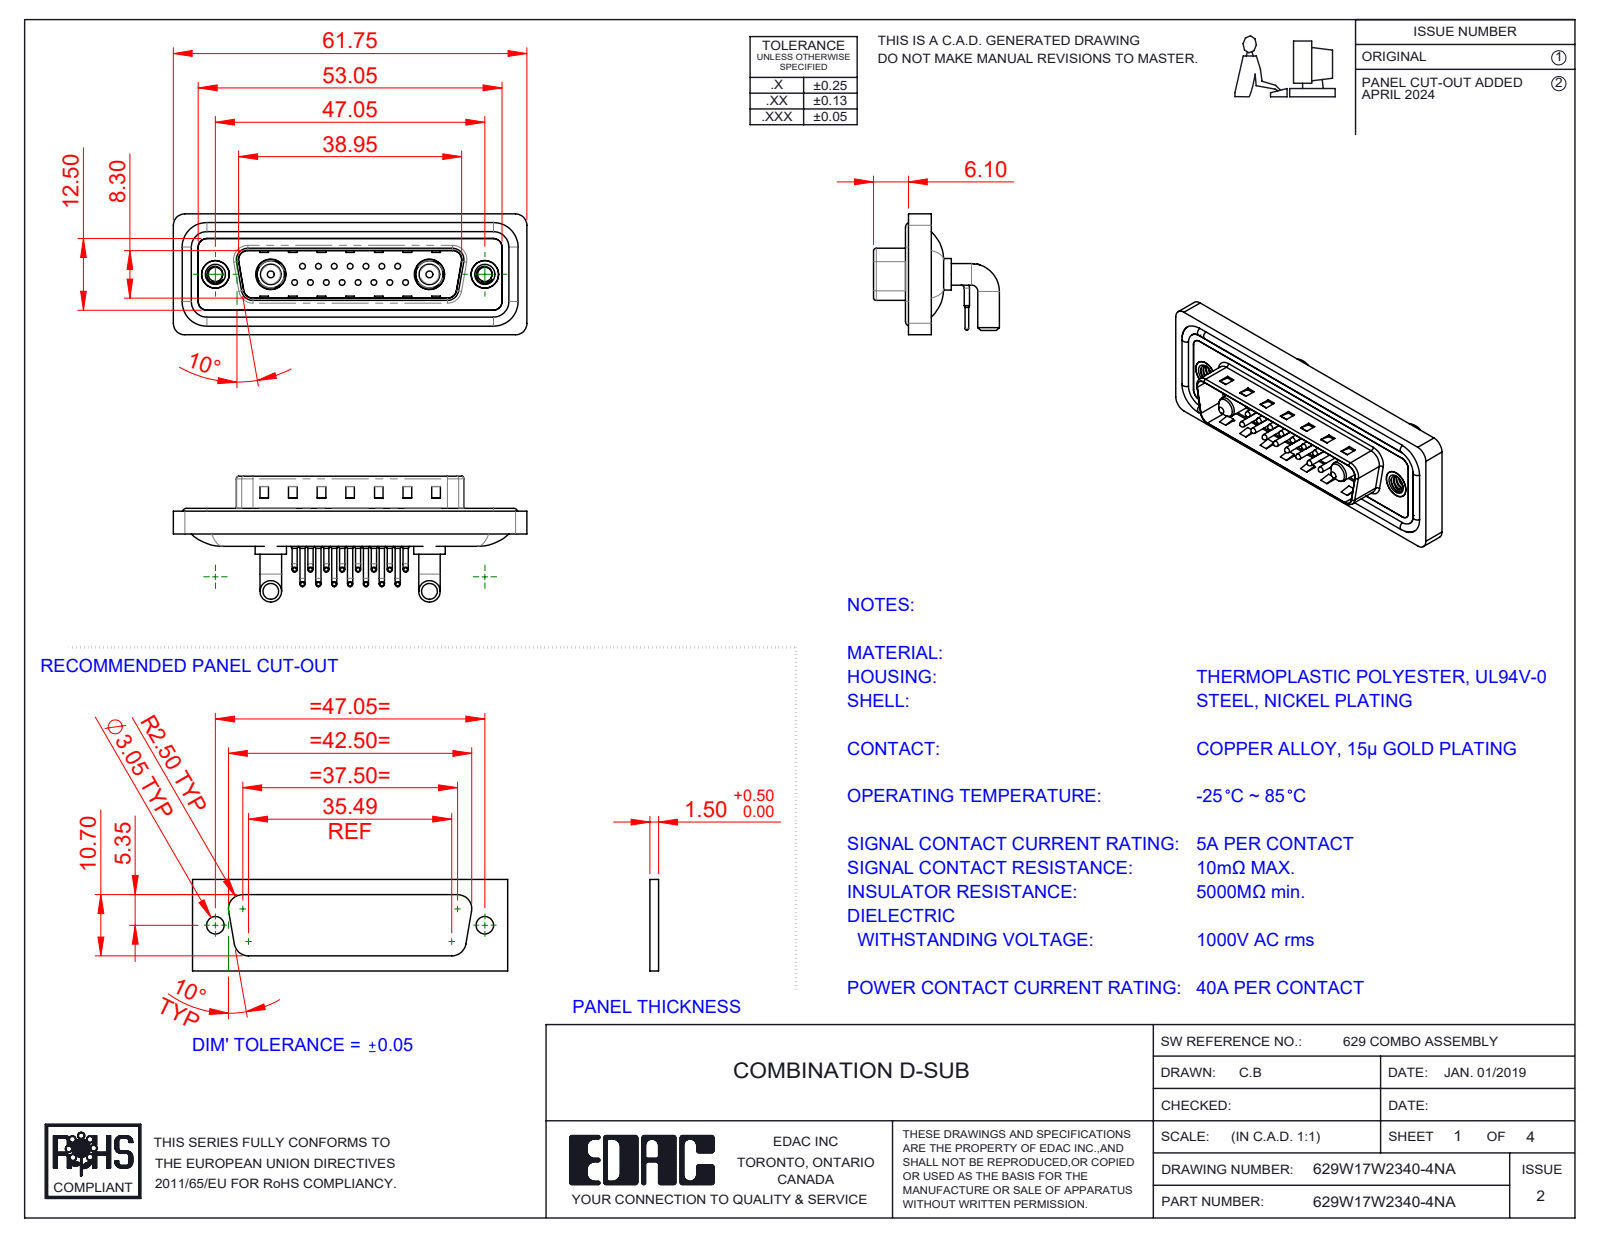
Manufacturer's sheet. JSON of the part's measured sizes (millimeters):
{"part_name": "629Combo Threaded Rivet_A; 629W17W2340-4NA; 629Combo Contact Row 1; 629Combo Waterproof Housing_25 Contacts (+5 more)", "step_written_by": "SolidWorks 2023 (CONFIG_CONTROL_DESIGN)", "units": "millimeters", "bodies": {"solids": 26, "faces": 2213, "planar": 1189, "cylindrical": 768, "other": 256}, "overall_size": [61.75, 21.98, 21.1], "volume_mm3": 7662, "surface_area_mm2": 12692, "round_holes": [[0.75, 15], [1.6, 15], [2, 15], [2.5, 2], [4, 2], [4.8, 2], [4.85, 2], [5, 2], [5.3, 2]], "round_bosses_or_shafts": [[0.9, 30], [1.5, 15], [1, 15], [0.65, 15], [3.75, 4], [1.6, 4], [5.5, 2], [5.2, 2]], "partial_cylinders_radius": [[1.5, 18], [2, 18], [1.01, 15], [0.5, 8], [1.6, 8], [0.25, 4], [0.6, 4], [0.65, 4]], "face_to_face_distances": [0.4, 2.9, 0.8, 4.1, 1.1, 2.1, 1.6, 4.5, 1.5, 2.5], "hole_center_spacings": [3.16, 2.77, 5.54, 8.31, 5.04, 7.49, 11.08, 5.03]}
